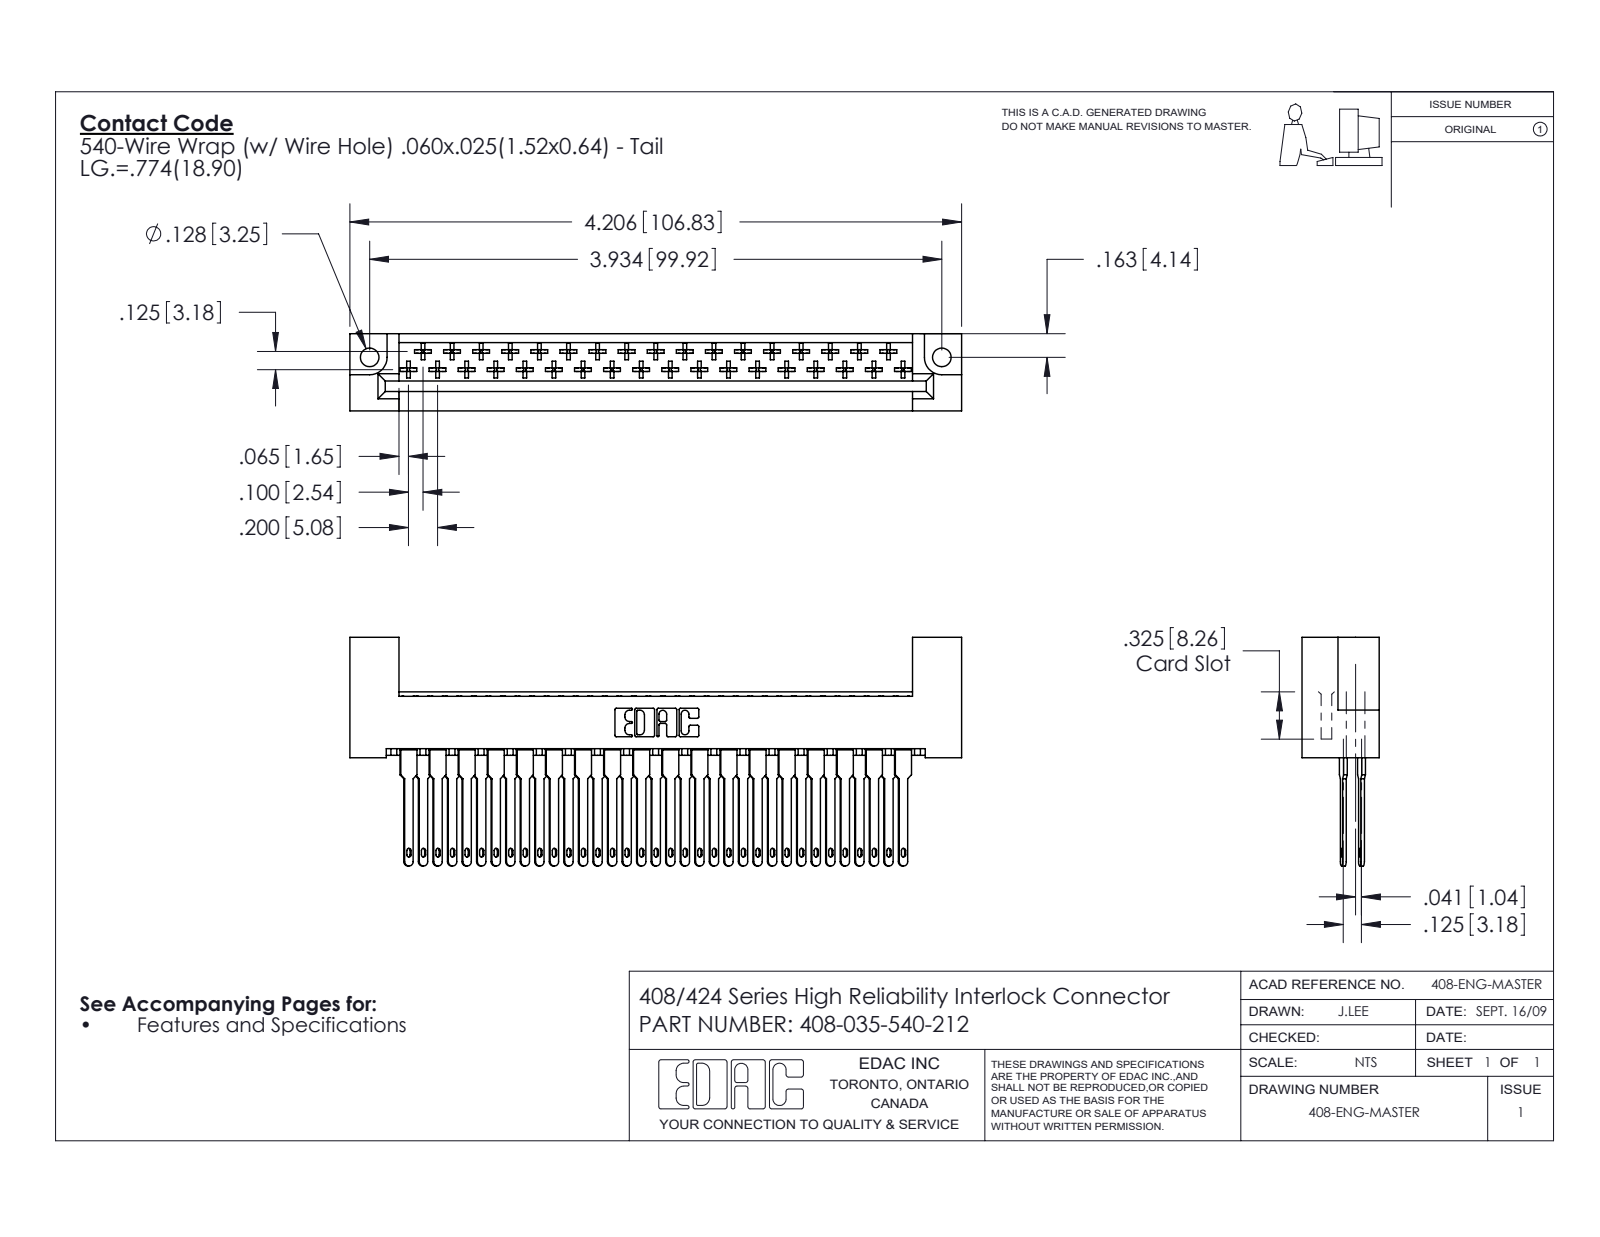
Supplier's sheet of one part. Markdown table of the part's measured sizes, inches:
| quantity | value |
| --- | --- |
| part name | 408-035-540-212; 408 Part_035 - 2; 408-290-001_408-290-140 |
| STEP written by | SolidWorks 2016 (CONFIG_CONTROL_DESIGN) |
| units | inches |
| bodies | 36 solids, 2134 faces (1559 planar, 435 cylindrical, 140 other) |
| overall size | 4.206 × 1.572 × 0.531 |
| volume | 0.852 in³ |
| surface area | 27.95 in² |
| round holes (diameter × count) | 0.128 × 2 |
| partial cylindrical surfaces (radius × count) | 0.01 × 210, 0.015 × 70, 0.02 × 37, 0.03 × 35, 0.01 × 22, 0.007 × 6, 0.031 × 6, 0.026 × 3 |
| main face-to-face distances | 0.531, 0.125, 0.1, 0.025, 0.025, 0.361, 0.235, 0.259, 0.272, 0.217 |
| hole center spacings | 3.934 |
